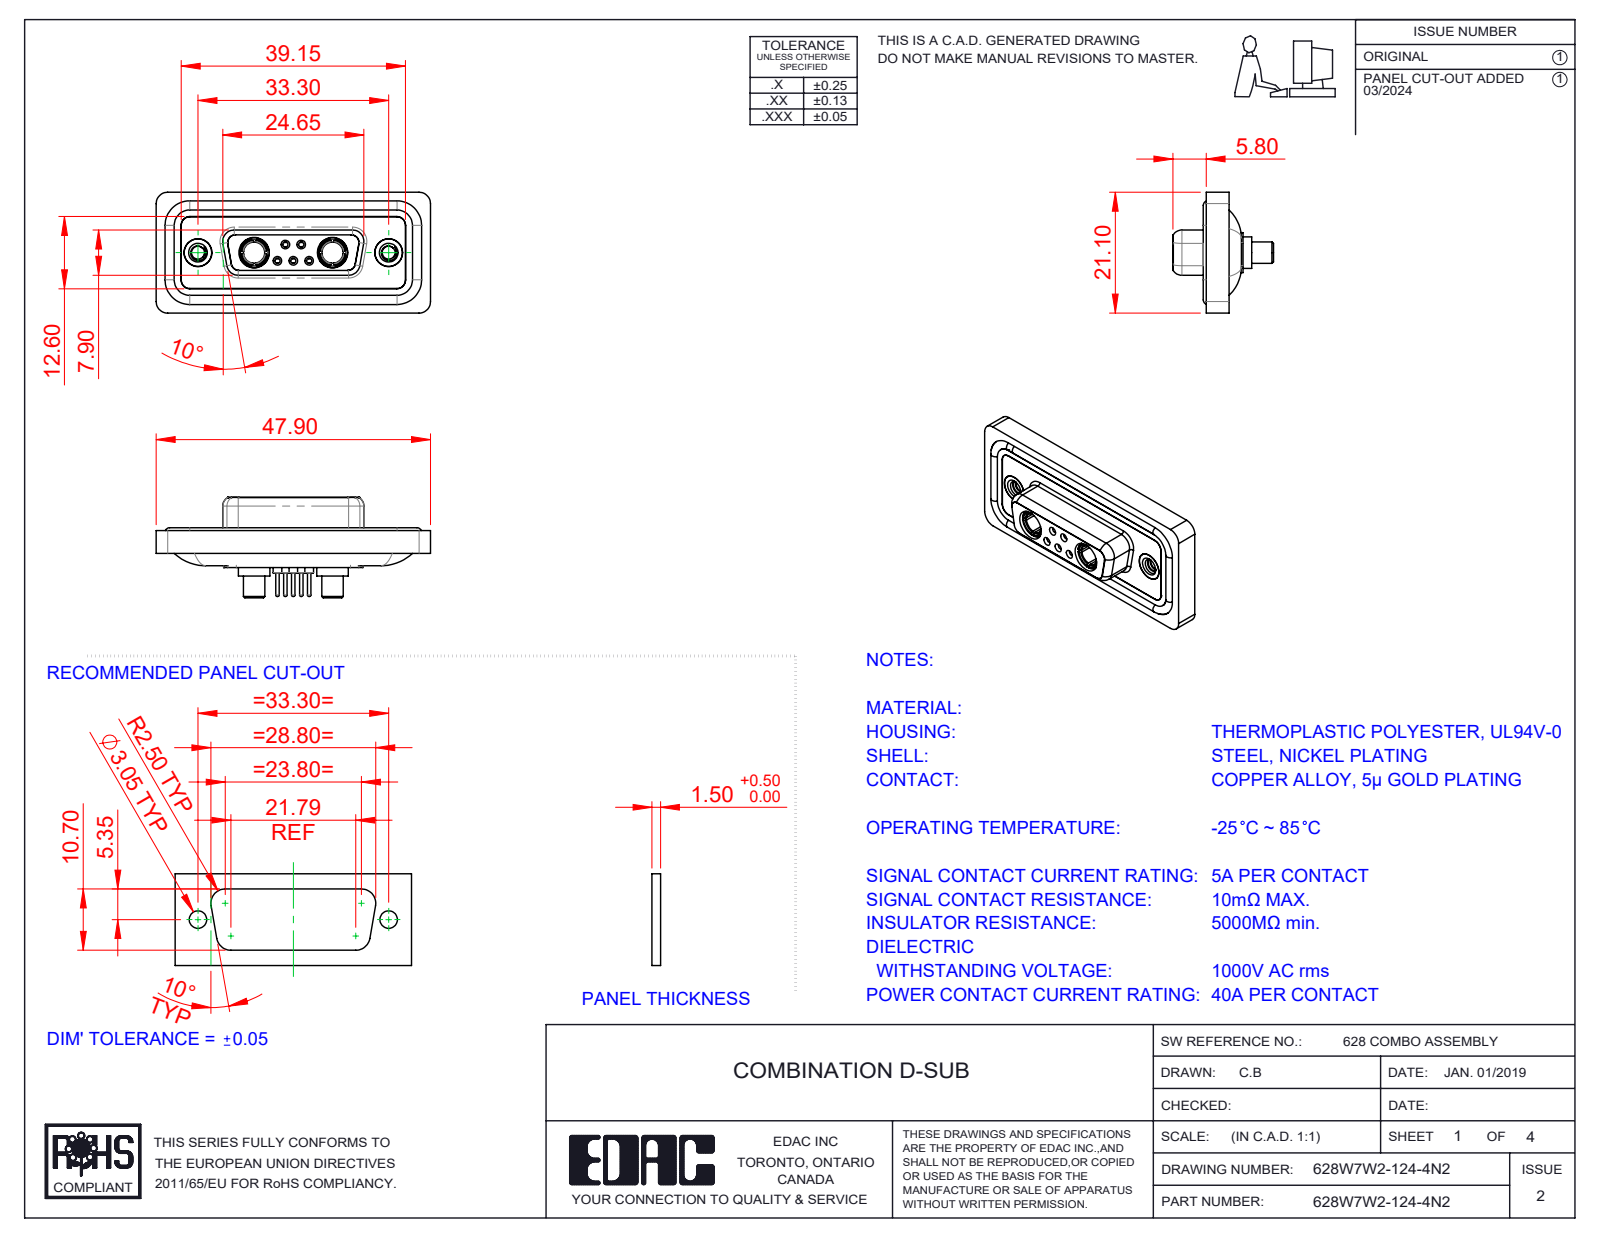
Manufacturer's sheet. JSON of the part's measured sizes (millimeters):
{"part_name": "628Combo Contact Row 1_24; 628Combo Waterproof Housing_15 Contacts; 628Combo Shell Front_15 Contacts; 628Combo Shell Rear_15 Contacts (+5 more)", "step_written_by": "SolidWorks 2023 (CONFIG_CONTROL_DESIGN)", "units": "millimeters", "bodies": {"solids": 16, "faces": 809, "planar": 238, "cylindrical": 329, "other": 242}, "overall_size": [47.9, 21.1, 17.55], "volume_mm3": 6114, "surface_area_mm2": 9907, "round_holes": [[0.9, 5], [1.1, 5], [1.5, 5], [2, 5], [4.85, 4], [1.6, 3], [1.7, 2], [2.26, 2], [3.7, 2], [4, 2], [4.05, 2], [5, 2]], "round_bosses_or_shafts": [[1.6, 6], [2.2, 5], [0.6, 5], [5.5, 2], [5.2, 2], [4.96, 2], [4.95, 2], [4.8, 2]], "partial_cylinders_radius": [[1.5, 22], [2, 20], [1.35, 12], [1.6, 8], [0.25, 4], [0.5, 4], [0.6, 4], [0.65, 4]], "face_to_face_distances": [0.4, 1.8, 1.6, 0.5, 2.9, 7.45, 1.1, 5.65, 6.6, 7.05], "hole_center_spacings": [3.16, 2.77, 9.8, 23.5, 4.31, 4.33, 5.03, 5.04]}
